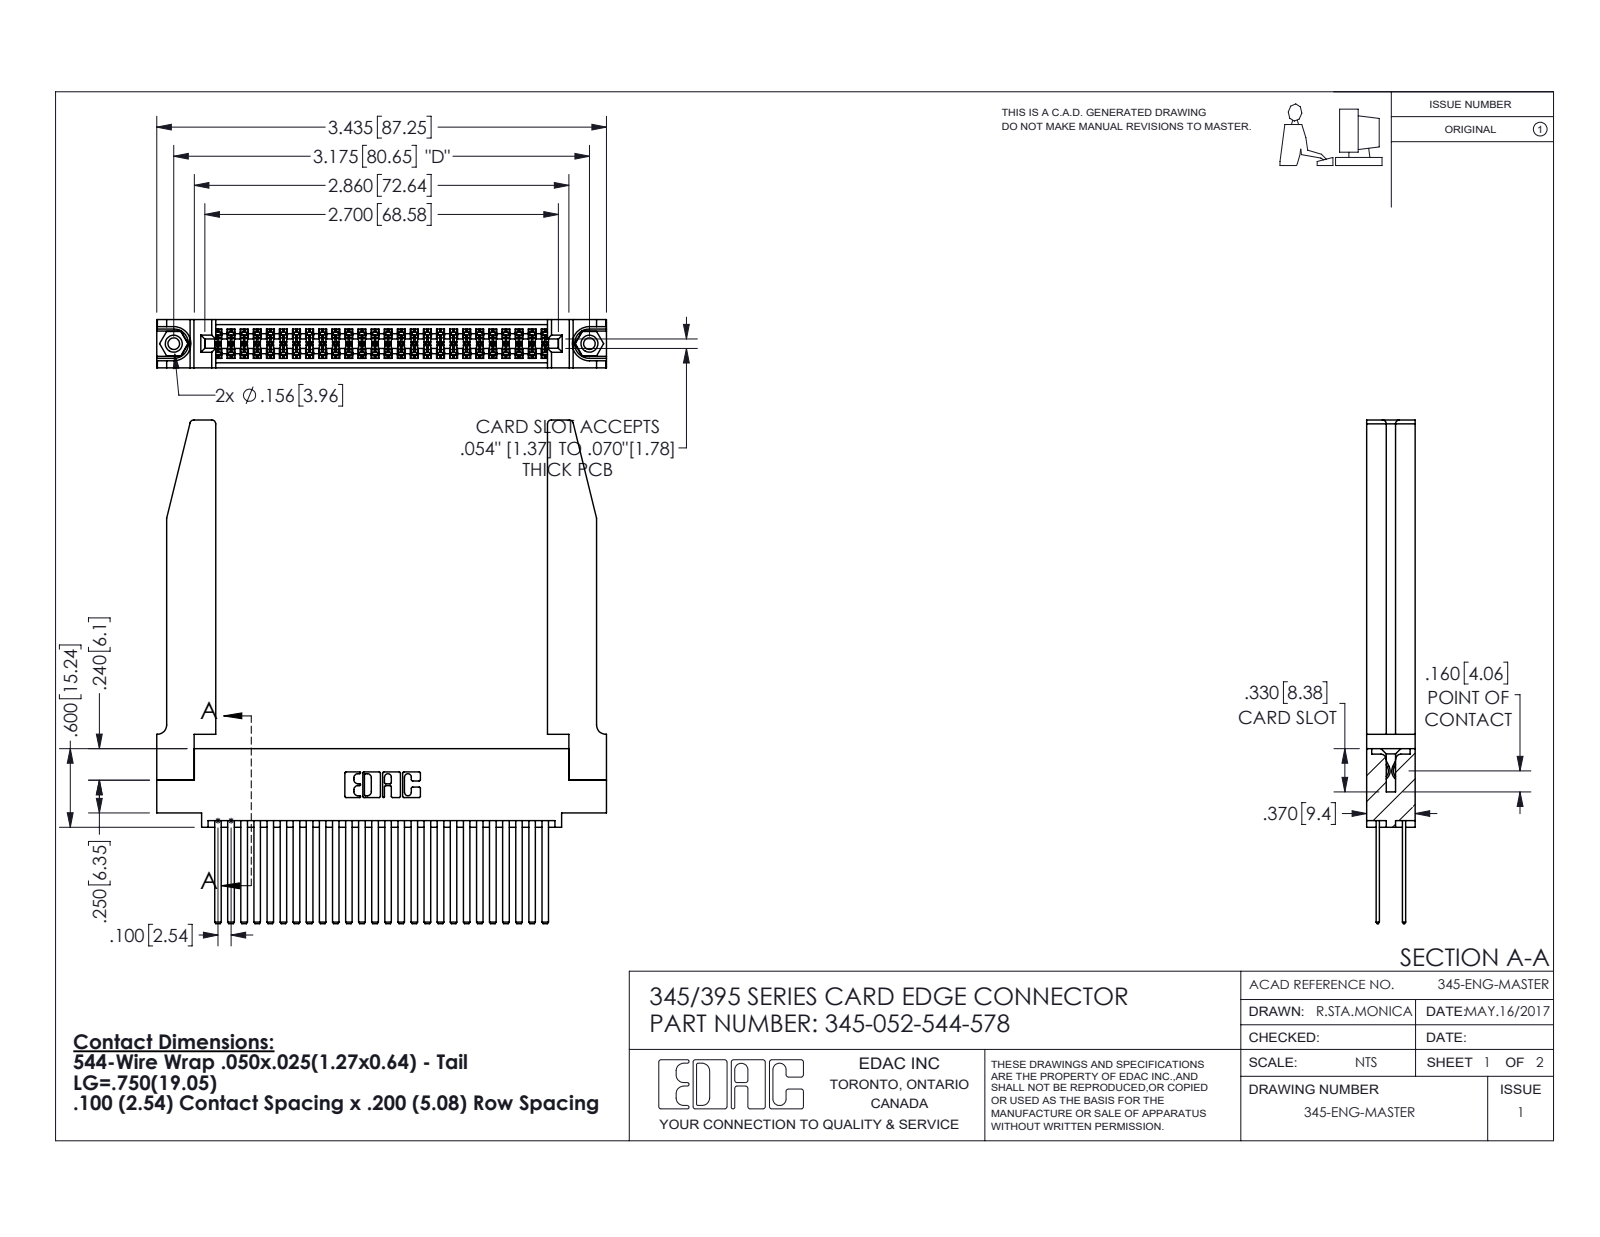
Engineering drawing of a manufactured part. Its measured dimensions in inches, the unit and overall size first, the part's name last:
Units: inches
Overall size (bounding box): 3.847 × 3.436 × 0.37
Round holes (diameter × count): ⌀0.089 ×2, ⌀0.125 ×2, ⌀0.156 ×2, ⌀0.064 ×1
Round bosses / shafts (diameter × count): ⌀0.155 ×2
Partial cylindrical surfaces — rounded edges, fillets, slot ends (radius × count): R0.006 ×78, R0.01 ×22, R0.03 ×8, R0.007 ×6, R0.031 ×6, R0.026 ×3, R0.014 ×2, R0.019 ×2
Main face-to-face distances: 0.072, 0.298, 0.37, 0.098, 0.272, 0.025, 0.2, 0.225, 0.175, 0.148
Hole centre spacings: 0.27, 2.94, 3.175
Volume: 1.022 in³ · Surface area: 34.16 in²
Bodies: 57 solids, 2652 faces (1734 planar, 866 cylindrical, 52 other)
Part name (STEP PRODUCT): 345-052-544-578; 345-220-078_345-220-078; 345-250-001_345-250-001-102; 345-292-001_345-293-144 (+1 more)
STEP written by: SolidWorks 2016 (CONFIG_CONTROL_DESIGN)
